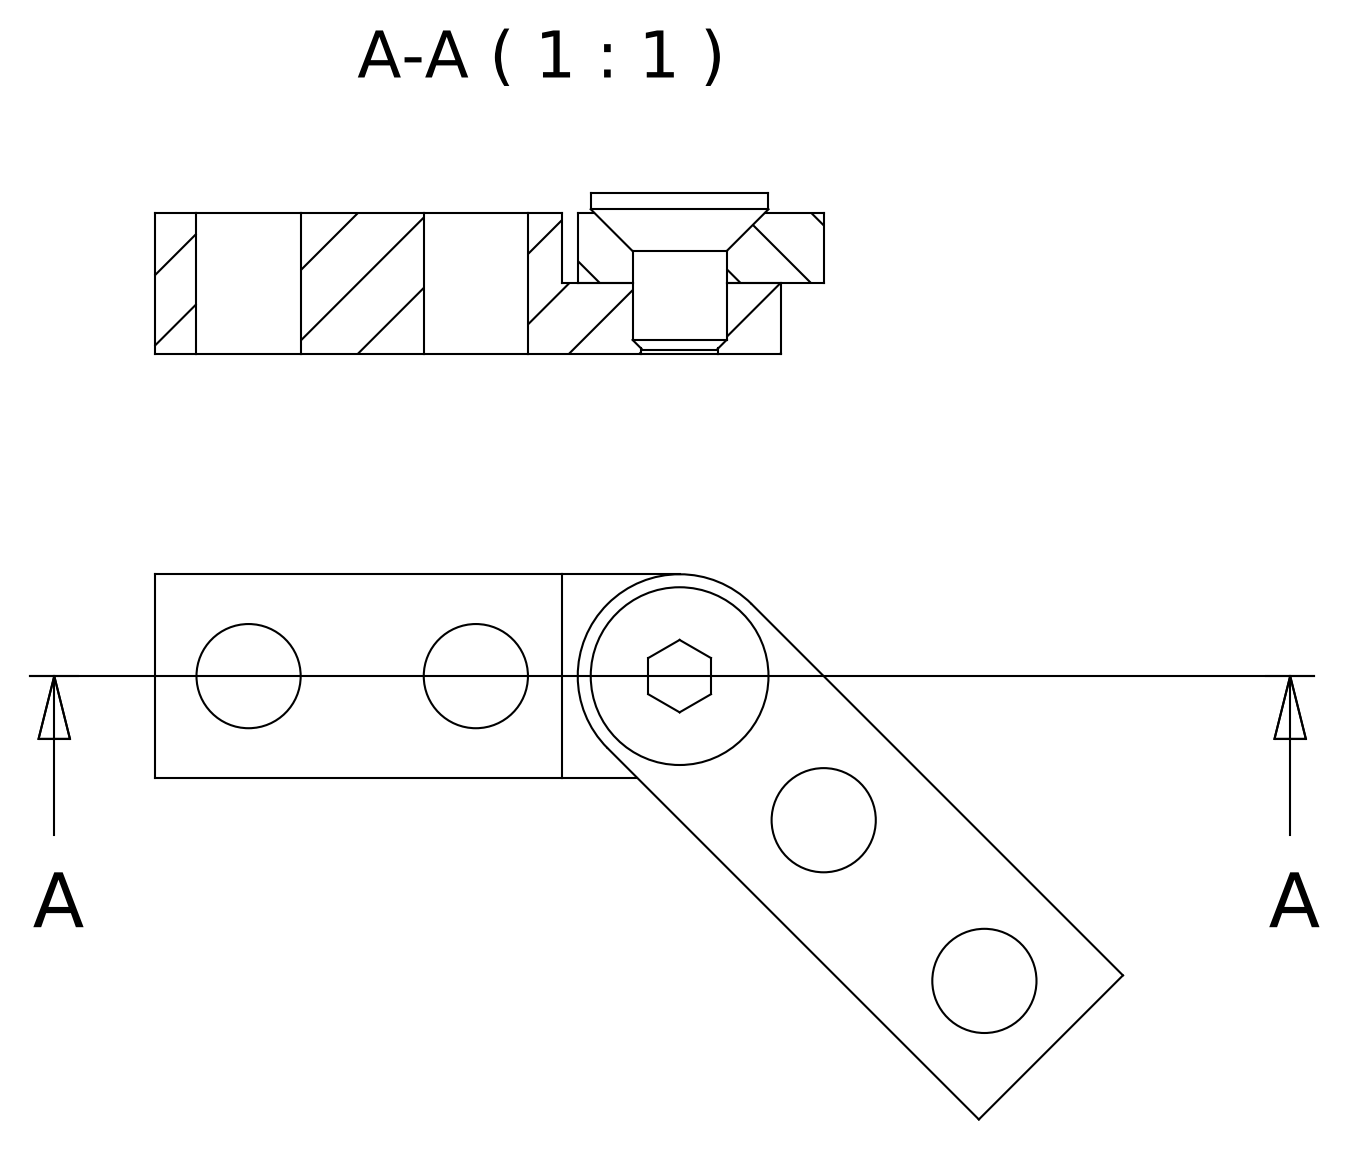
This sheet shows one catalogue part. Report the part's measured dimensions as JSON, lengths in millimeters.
{"part_name": "CGIPR0000015; 440000011892; 440000011893; ISO 10642 - M6 x 10", "step_written_by": "Autodesk Inventor 2019 (AUTOMOTIVE_DESIGN)", "units": "millimeters", "bodies": {"solids": 3, "faces": 36, "planar": 22, "cylindrical": 10, "other": 4}, "overall_size": [61.78, 34.78, 10.27], "volume_mm3": 6449, "surface_area_mm2": 4554, "round_holes": [[6.65, 4], [4.92, 1], [5.5, 1]], "round_bosses_or_shafts": [[13, 1], [11.34, 1], [6, 1]], "face_to_face_distances": [9, 4.5, 13, 10.27, 5.77, 1.27, 26, 25.99, 4, 4.23], "hole_center_spacings": [13, 14.5, 14.51, 24.02, 27.5, 27.51, 37.82, 37.83]}
